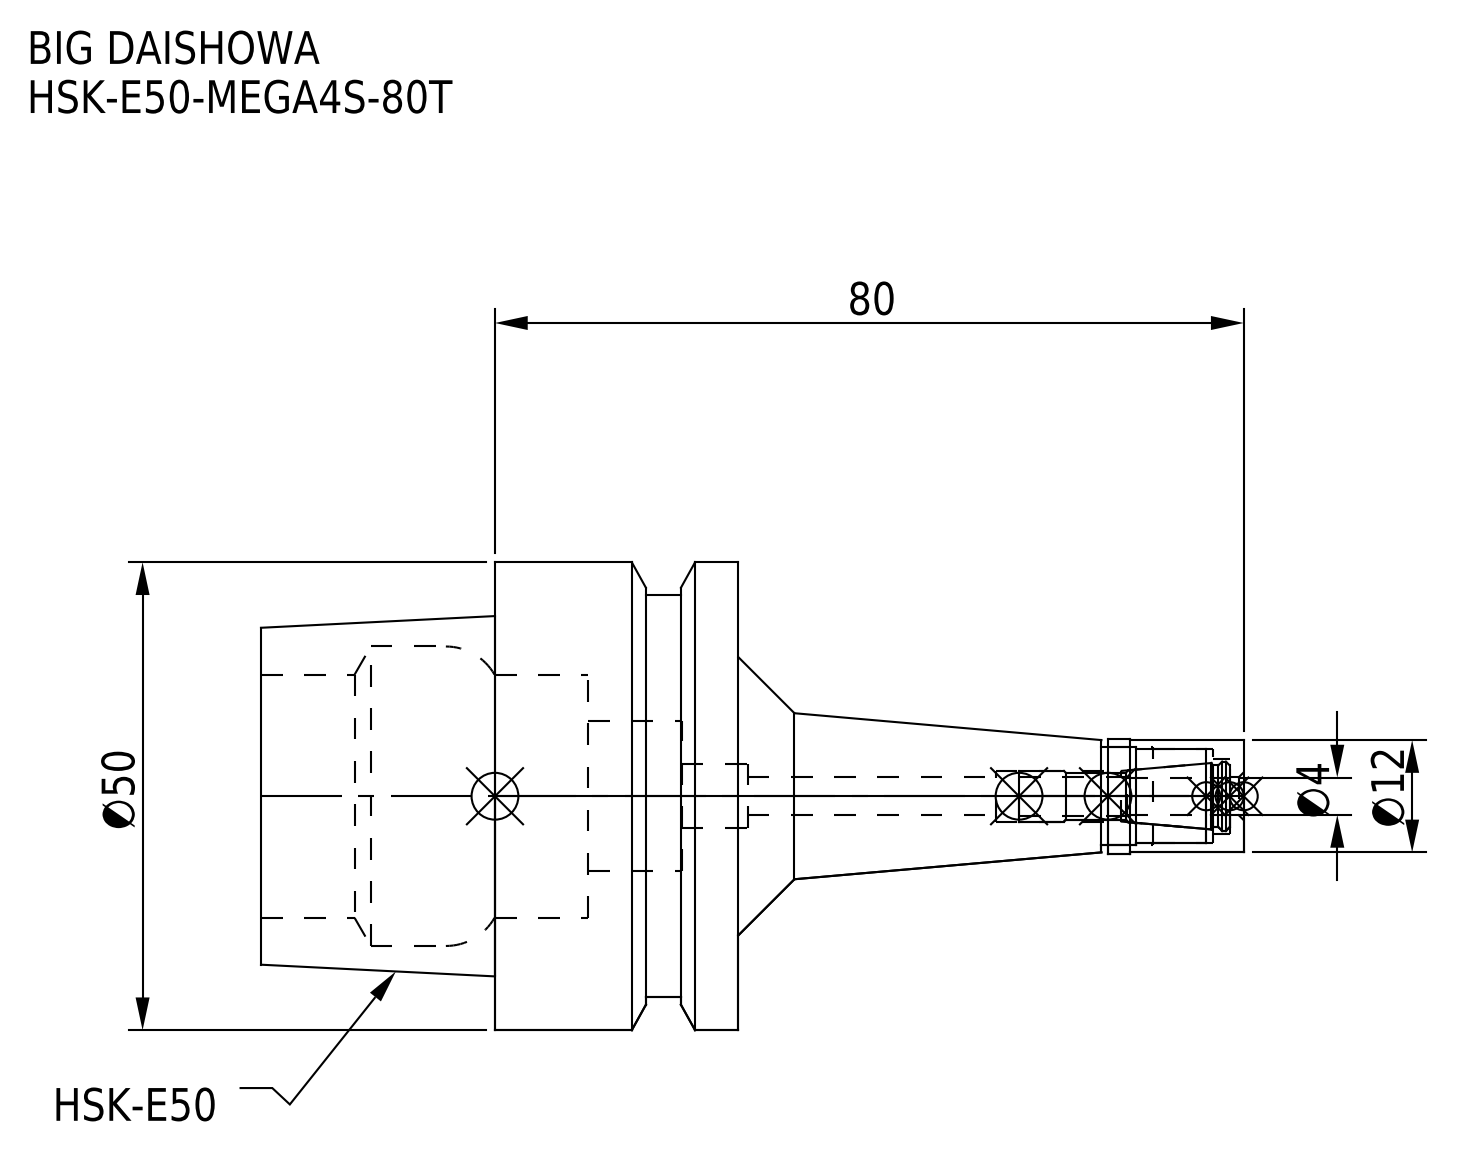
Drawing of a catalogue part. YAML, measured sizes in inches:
part_name: "DXF_TEMP_ASSY_ASM_4_ASM.stp; HSK-E50-MEGA4S-80T_1.stp; HSK-E50-MEGA4S-80T-040.stp; MGN4S_1.stp (+3 more)"
step_written_by: "SolidWorks 2019 (CONFIG_CONTROL_DESIGN)"
units: inches
bodies: {solids: 2, faces: 74, planar: 18, cylindrical: 38, other: 18}
overall_size: [4.134, 1.969, 1.969]
volume: 3.699
surface_area: 29.77
round_holes:
  - {diameter: 0.161, count: 1}
  - {diameter: 0.213, count: 1}
  - {diameter: 0.268, count: 1}
  - {diameter: 0.315, count: 1}
  - {diameter: 0.394, count: 1}
  - {diameter: 0.413, count: 1}
  - {diameter: 0.63, count: 1}
  - {diameter: 1.024, count: 1}
  - {diameter: 1.26, count: 1}
round_bosses_or_shafts:
  - {diameter: 1.969, count: 1}
  - {diameter: 1.693, count: 1}
  - {diameter: 0.484, count: 1}
  - {diameter: 0.472, count: 1}
face_to_face_distances: [1.024, 0.984, 2.008, 0.632, 0.392, 1.376, 0.394, 0.238, 0.785, 1.77]
